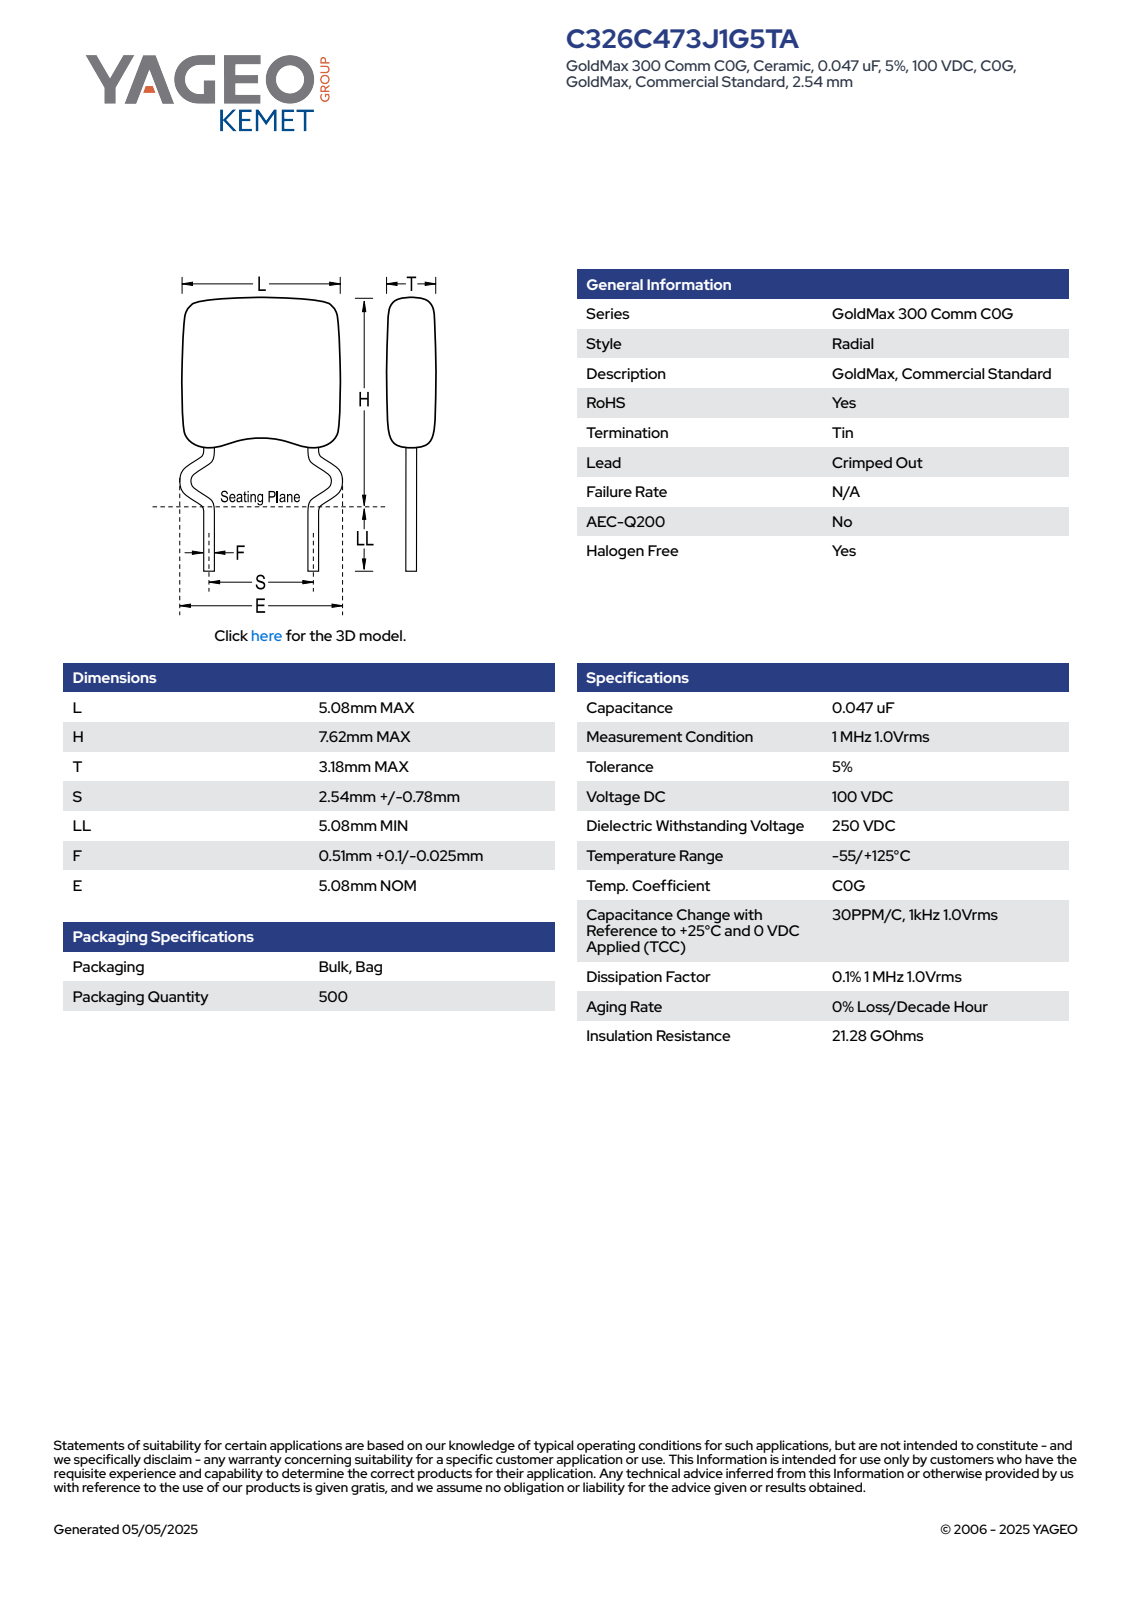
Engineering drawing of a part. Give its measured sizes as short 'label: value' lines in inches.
name: CCR_RCCR_C326_L5.08H7.62T3.18S2.54LL5.08F0.51E5.08
written by: SolidWorks 2014 (AUTOMOTIVE_DESIGN)
unit: in
bodies: 4 solids, 104 faces (66 planar, 16 cylindrical, 22 other)
size: 0.5 × 0.2 × 0.126
volume: 0.005 in³; area: 0.203 in²
bosses: 2× ⌀0.02
rounds: 8× R0.01, 4× R0.03
face distances: 0.125, 0.2, 0.189, 0.126, 0.311, 0.5, 0.08, 0.032, 0.42, 0.109
